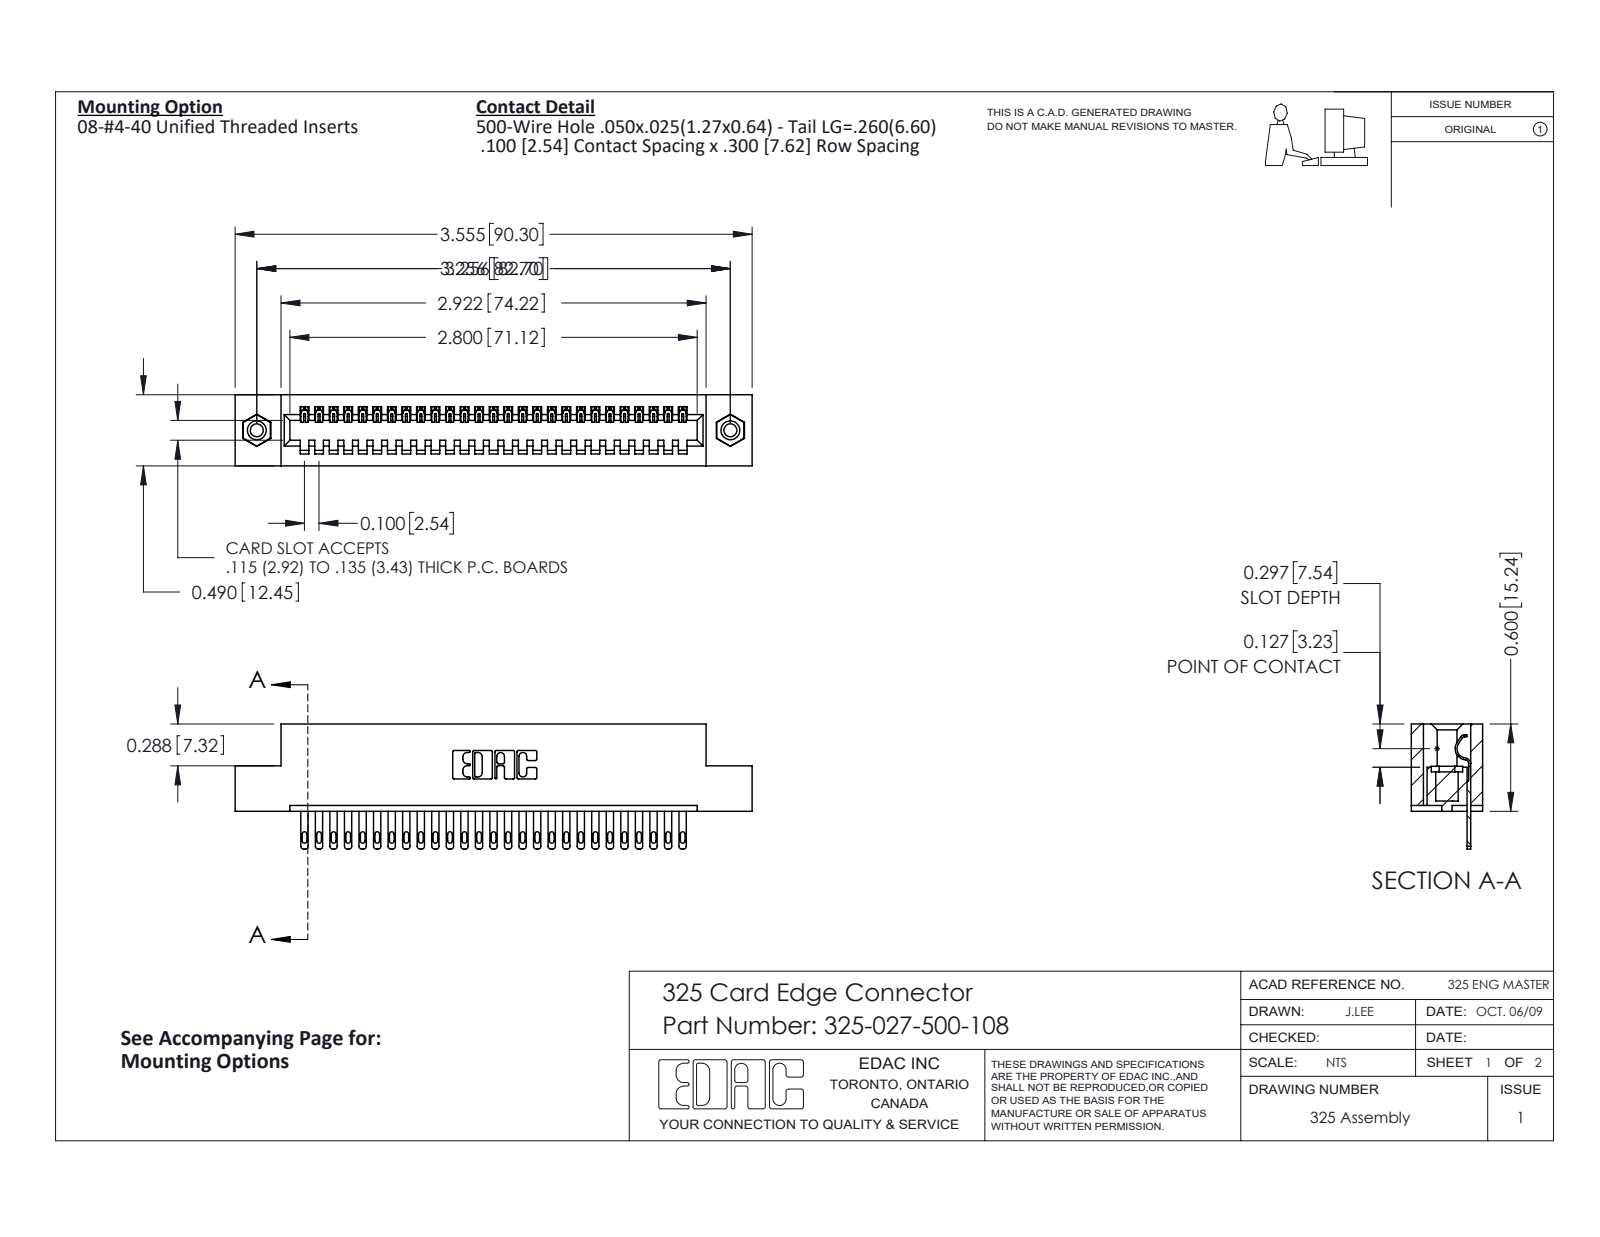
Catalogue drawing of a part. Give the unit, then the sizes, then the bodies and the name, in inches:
Units: inches
Overall size (bounding box): 3.555 × 0.86 × 0.49
Round holes (diameter × count): ⌀0.089 ×2, ⌀0.125 ×2, ⌀0.16 ×2
Round bosses / shafts (diameter × count): ⌀0.155 ×2
Partial cylindrical surfaces — rounded edges, fillets, slot ends (radius × count): R0.006 ×54, R0.016 ×54, R0.02 ×54, R0.01 ×22, R0.007 ×6, R0.031 ×6, R0.026 ×3, R0.014 ×1
Main face-to-face distances: 0.083, 0.407, 0.3, 0.49, 0.107, 0.383, 0.025, 0.04, 0.325, 0.1
Hole centre spacings: 3.256
Volume: 0.693 in³ · Surface area: 18.96 in²
Bodies: 30 solids, 1632 faces (1074 planar, 542 cylindrical, 16 other)
Part name (STEP PRODUCT): 325-027-500-108; 325-292-001_325-293-100; 345-250-001_345-250-003-102; 325 Part_TI
STEP written by: SolidWorks 2016 (CONFIG_CONTROL_DESIGN)
